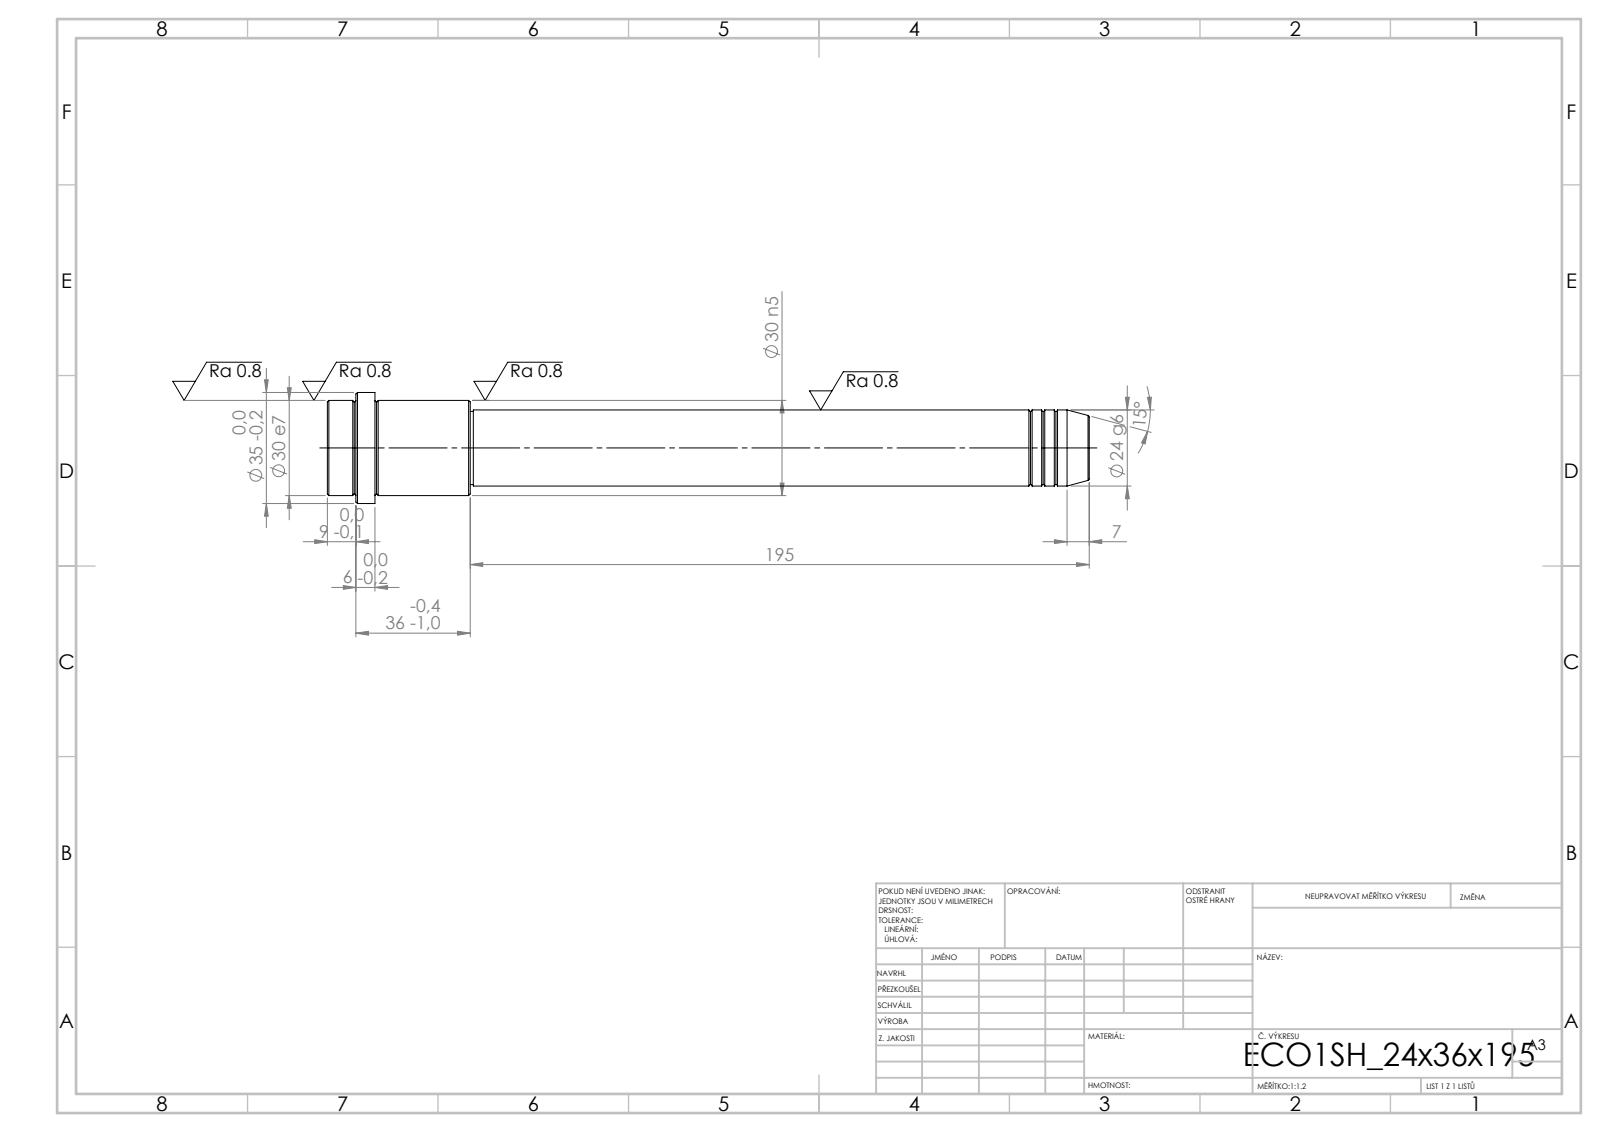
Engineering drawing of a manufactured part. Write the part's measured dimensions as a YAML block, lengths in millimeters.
step_written_by: "SolidWorks 2019 (CONFIG_CONTROL_DESIGN)"
units: millimeters
bodies: {solids: 1, faces: 52, planar: 6, cylindrical: 16, other: 30}
overall_size: [240, 35, 35]
volume: 120851
surface_area: 21004
round_bosses_or_shafts:
  - {diameter: 35, count: 1}
  - {diameter: 30, count: 1}
  - {diameter: 24, count: 1}
  - {diameter: 23, count: 1}
face_to_face_distances: [240, 225, 15, 195, 30, 45, 231, 36, 6, 9]
